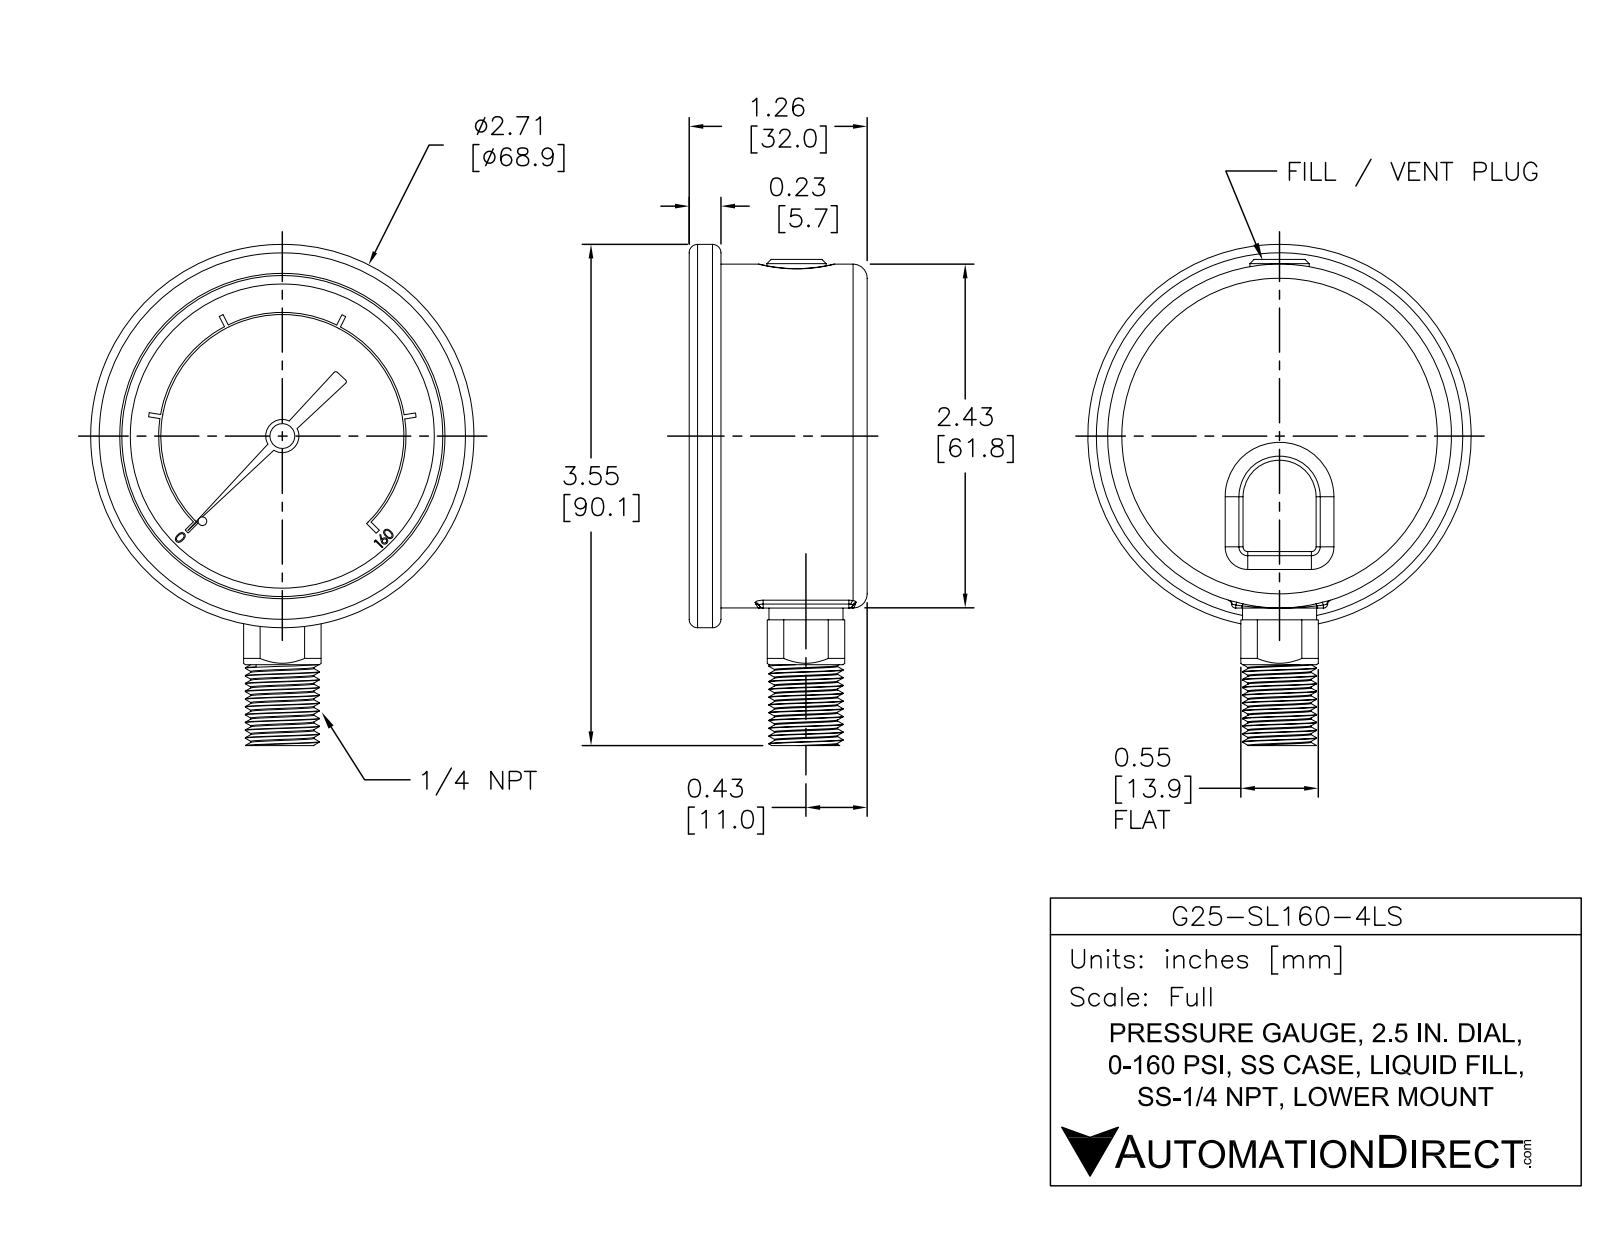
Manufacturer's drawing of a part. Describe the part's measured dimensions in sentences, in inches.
The part is named "G25-SL160-4LS". Its 3-D file was written by "SolidWorks 2021 (AUTOMOTIVE_DESIGN)". It is 1 solid with 346 faces: 198 planar, 85 cylindrical and 63 other. Overall it measures 3.546 by 2.713 by 1.26 inches. Its volume is 5.273 cubic inches and its surface area 24.68 square inches. Round holes: 1 of diameter 0.027, 1 of diameter 0.071, 1 of diameter 0.119, 1 of diameter 2.272. Round bosses or shafts: 1 of diameter 2.713, 1 of diameter 2.433, 1 of diameter 0.524, 1 of diameter 0.42, 1 of diameter 0.235, 1 of diameter 0.176, 1 of diameter 0.14, 1 of diameter 0.041. Partial cylindrical surfaces (rounded edges, fillets, slot ends): 9 of radius 0.03, 3 of radius 0.1, 2 of radius 0.015, 1 of radius 0.316, 1 of radius 0.86, 1 of radius 0.875. The main face-to-face distances are 1.01, 1.26, 0.25, 1.035, 0.025, 0.225, 0.1, 0.91, 0.935, 1.16. The hole center spacings are 0.067.
